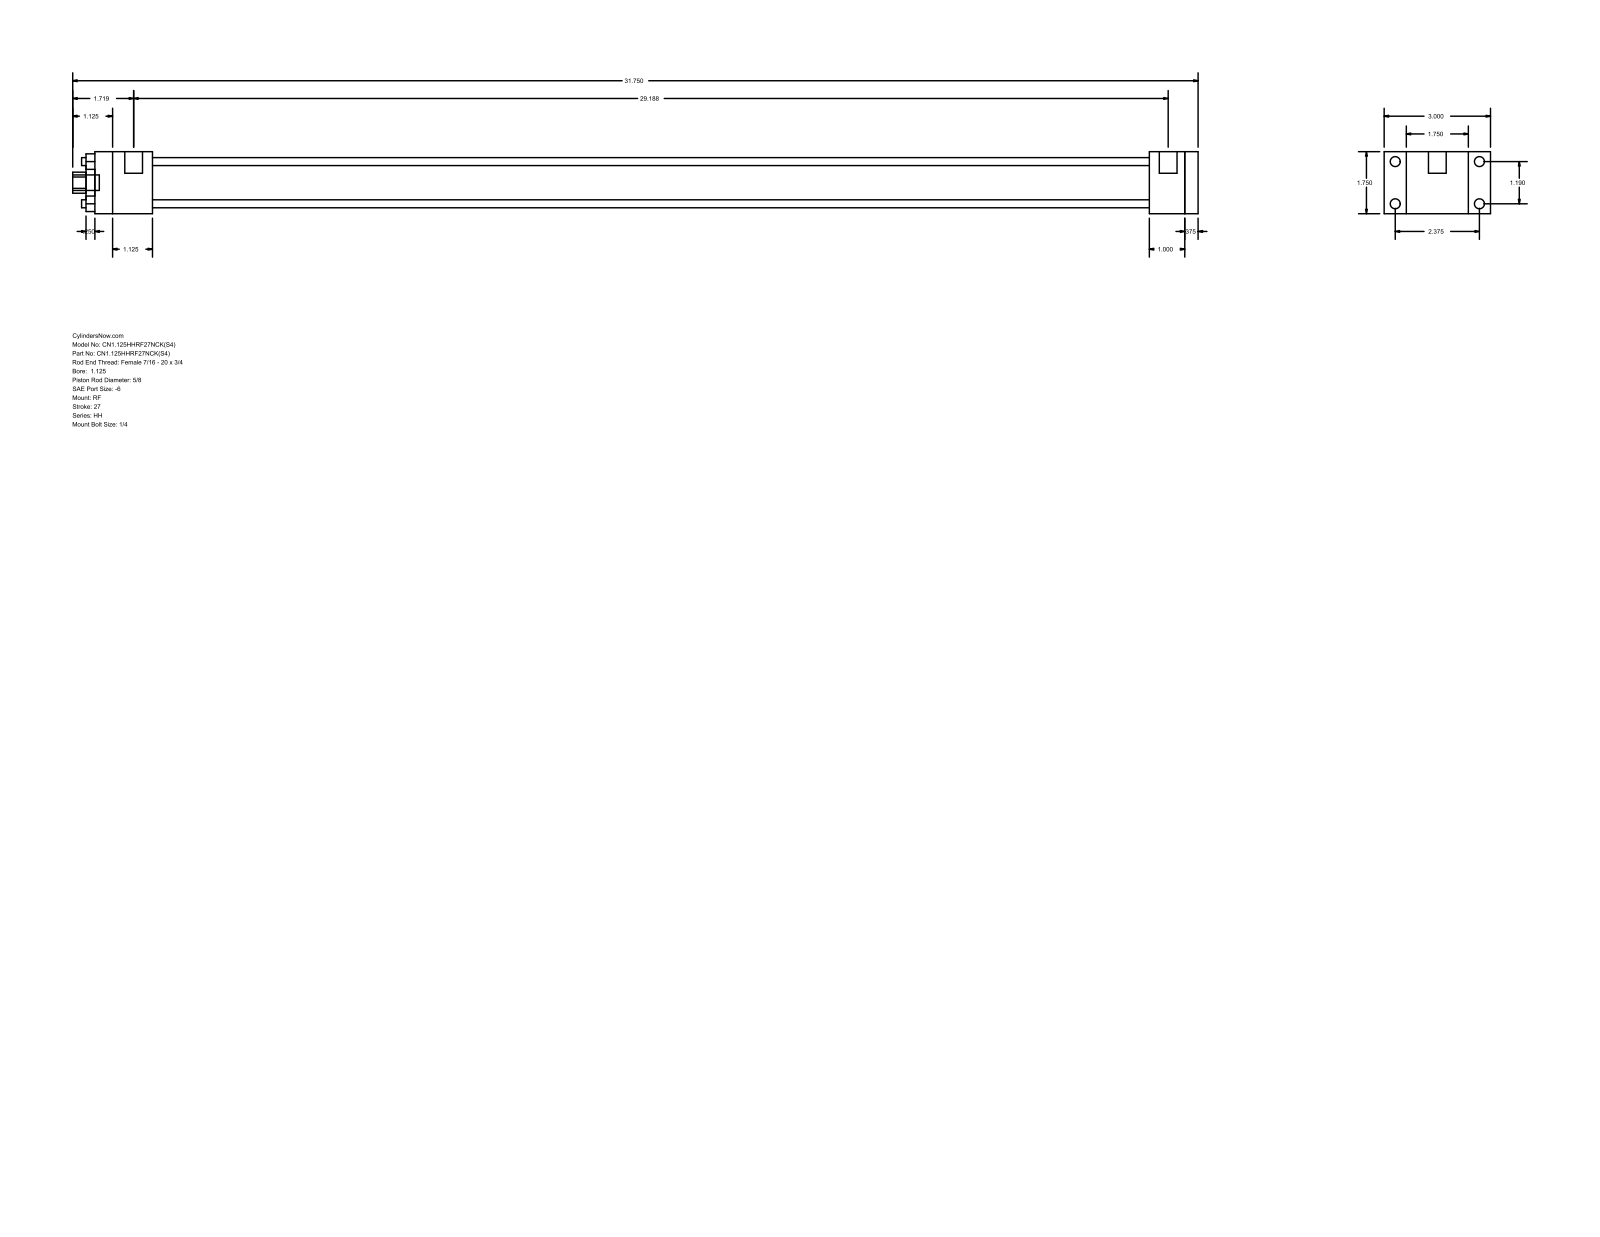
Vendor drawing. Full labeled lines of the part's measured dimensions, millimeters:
Part name (STEP PRODUCT): HH_RF__0112_0.625
STEP written by: GSSL Pune (CONFIG_CONTROL_DESIGN)
Units: millimetres
Bodies: 0 solids, 92 faces (64 planar, 28 cylindrical, 0 other)
Overall size (bounding box): 806.45 × 76.2 × 44.45
Round holes (diameter × count): ⌀5.71 ×4, ⌀15.88 ×1, ⌀28.57 ×1, ⌀34.92 ×1
Round bosses / shafts (diameter × count): ⌀7.14 ×4, ⌀5.56 ×4, ⌀12.7 ×2, ⌀11.11 ×1
Partial cylindrical surfaces — rounded edges, fillets, slot ends (radius × count): R7.54 ×1
Main face-to-face distances: 44.46, 9.53, 790.57, 15.87, 739.77, 749.3, 714.37, 25.4, 34.93, 41.27
Hole centre spacings: 21.37, 30.22, 42.74
